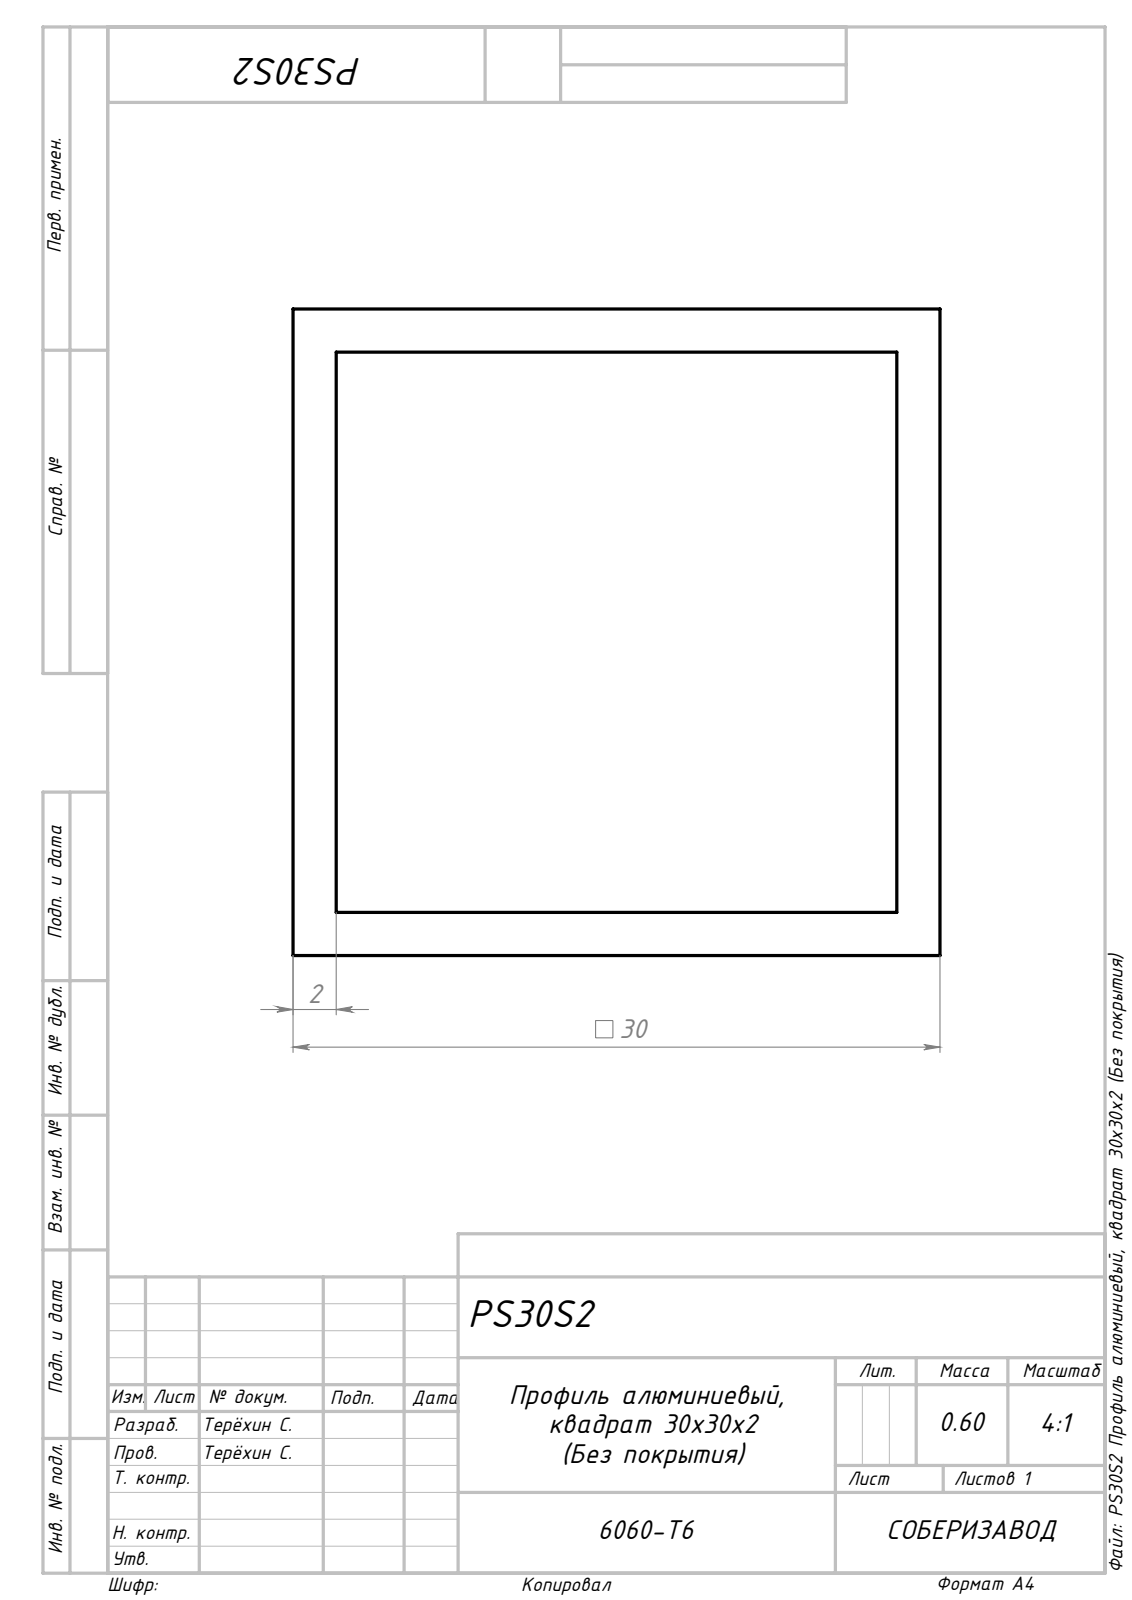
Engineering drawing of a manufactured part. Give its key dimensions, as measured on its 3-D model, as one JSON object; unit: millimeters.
{"part_name": "Сборка1; PS30S2 Профиль алюминиевый, квадрат 30x30x2 (Без покрытия)_00", "step_written_by": "SolidWorks 2024 (AUTOMOTIVE_DESIGN)", "units": "millimeters", "bodies": {"solids": 1, "faces": 10, "planar": 10, "cylindrical": 0, "other": 0}, "overall_size": [1000, 30, 30], "volume_mm3": 224000, "surface_area_mm2": 224448, "face_to_face_distances": [2, 28, 30, 26, 1000]}
